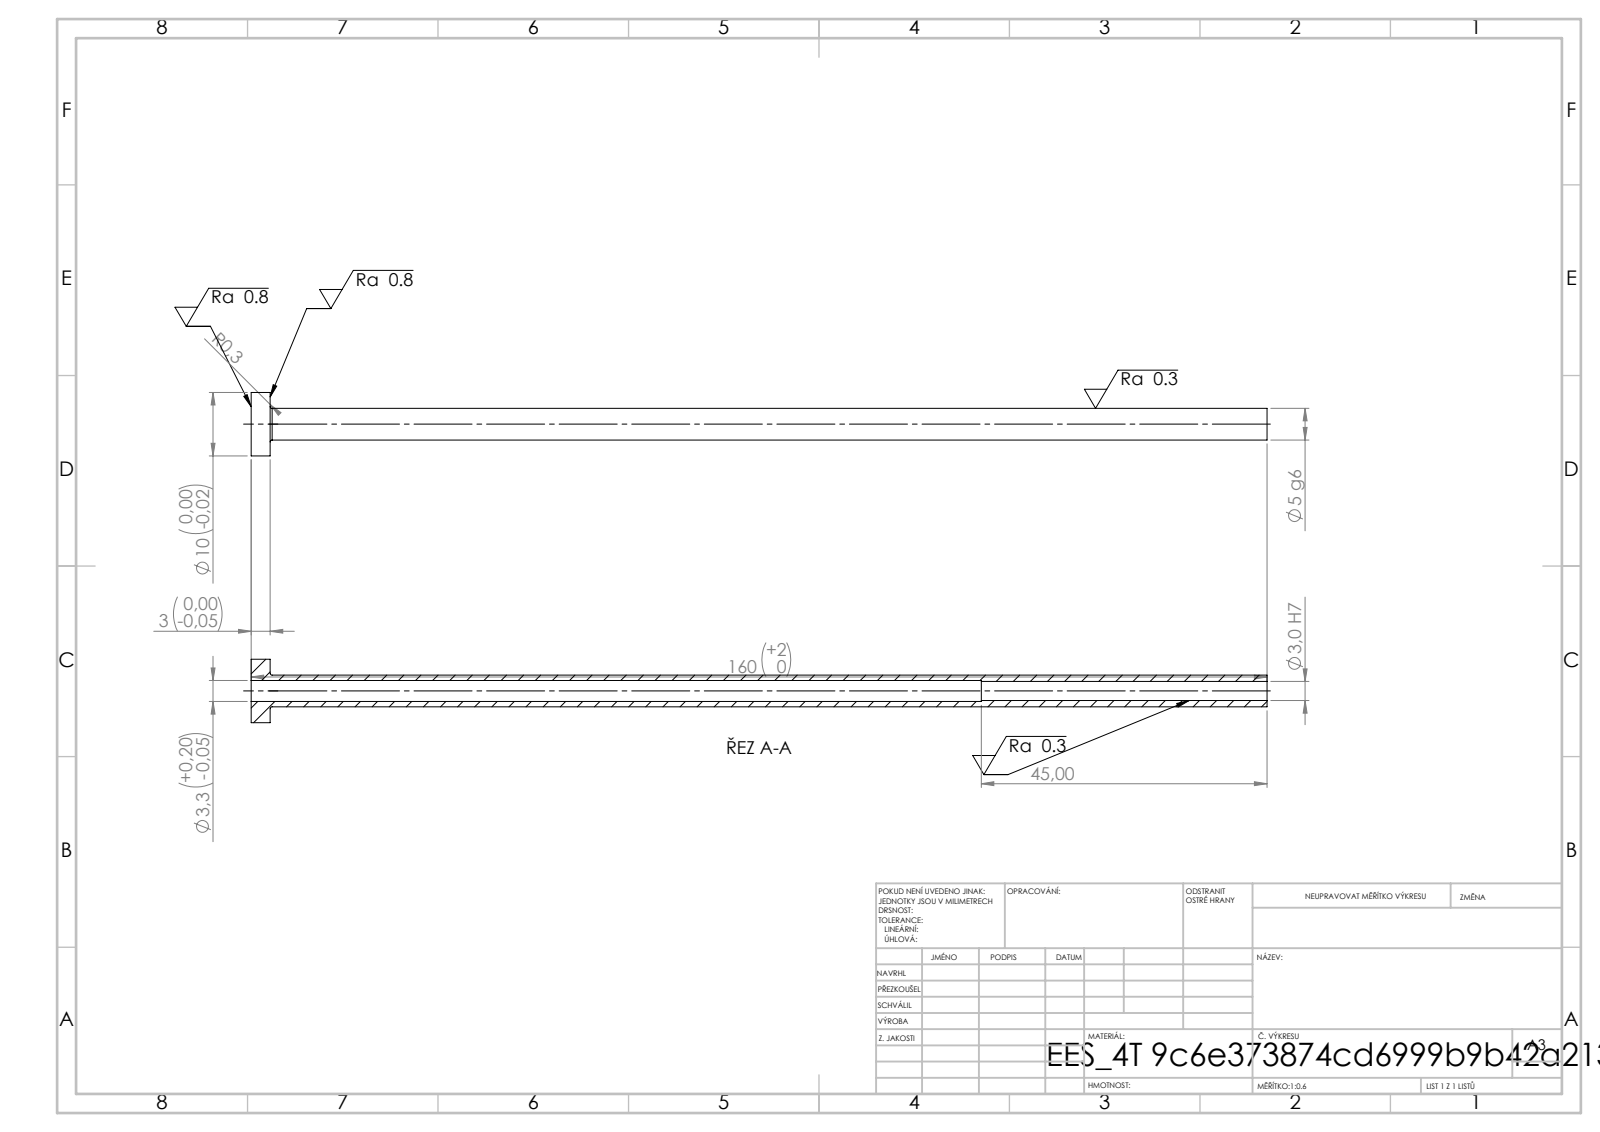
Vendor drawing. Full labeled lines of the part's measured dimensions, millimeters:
STEP written by: SolidWorks 2019 (CONFIG_CONTROL_DESIGN)
Units: millimetres
Bodies: 1 solid, 14 faces (4 planar, 8 cylindrical, 2 other)
Overall size (bounding box): 160 × 10 × 10
Volume: 2 017 mm³ · Surface area: 4 318 mm²
Round holes (diameter × count): ⌀3 ×1, ⌀3.3 ×1
Round bosses / shafts (diameter × count): ⌀10 ×1, ⌀5 ×1
Main face-to-face distances: 3, 160, 157, 115, 112, 45
